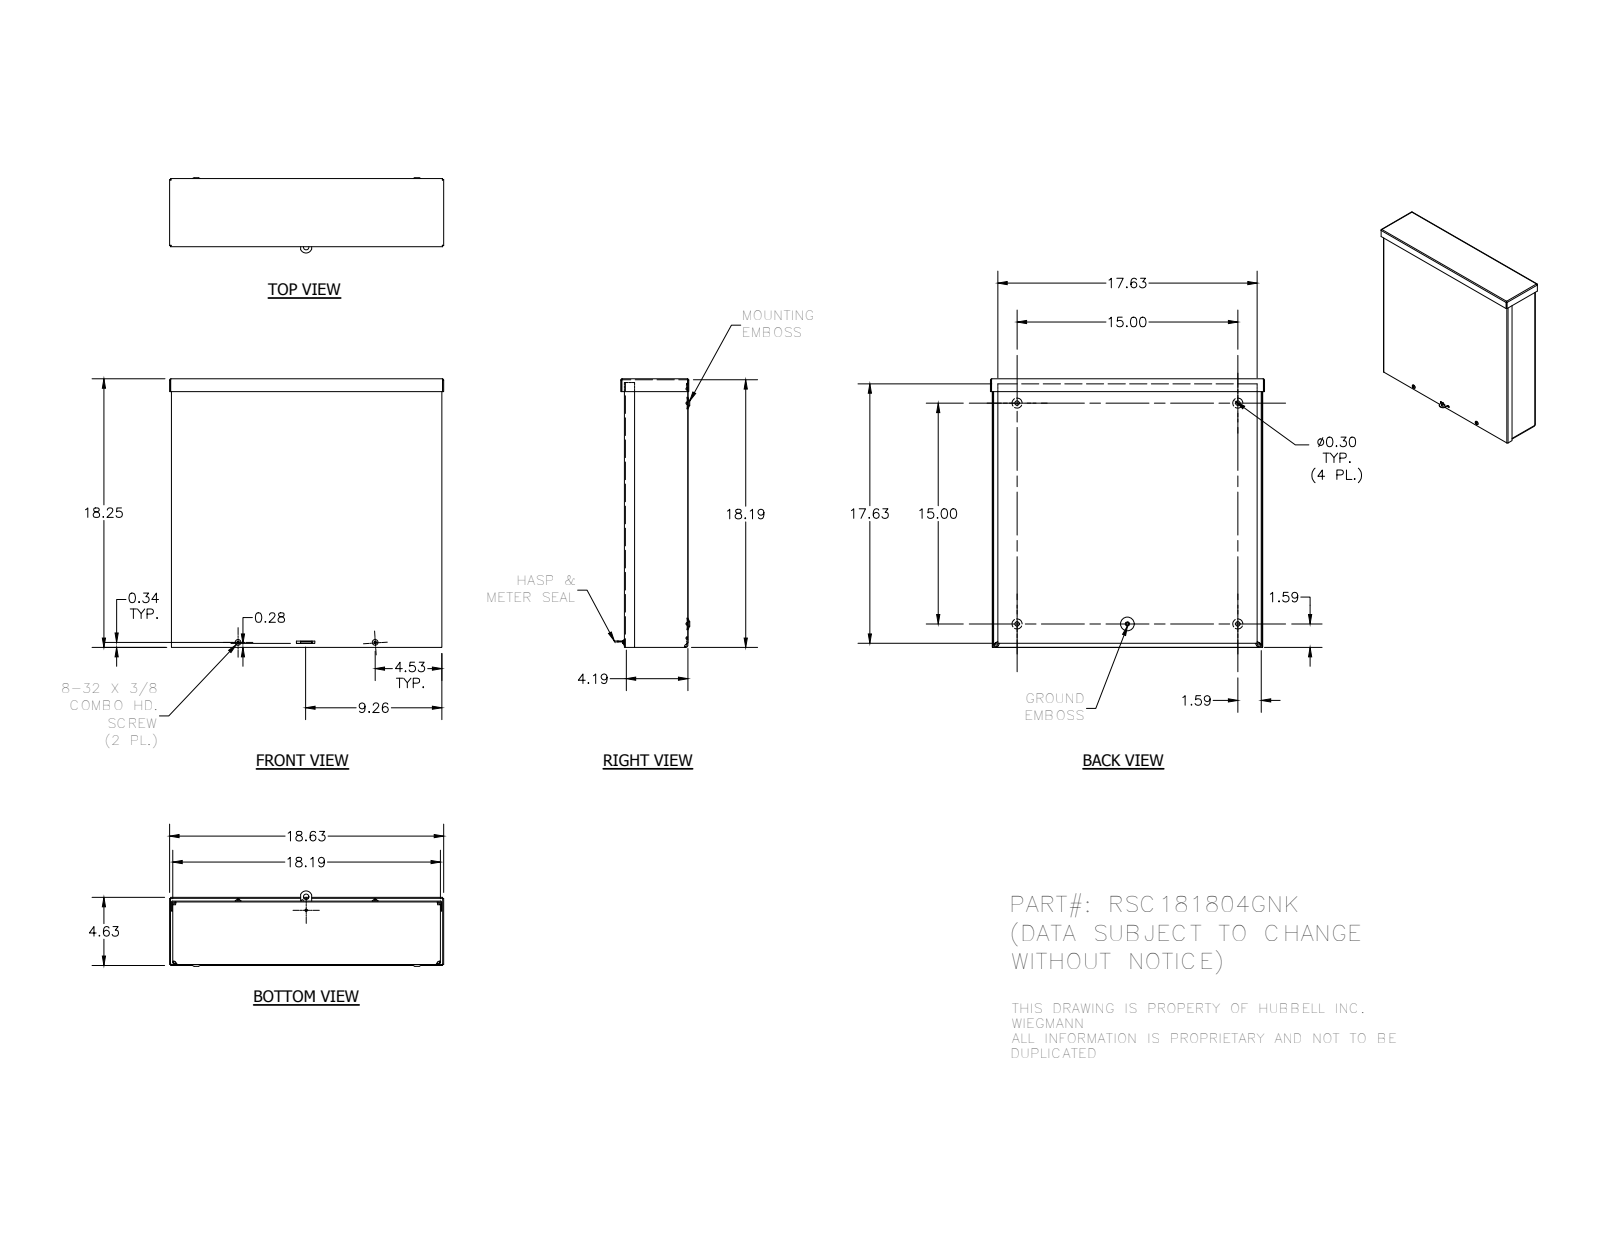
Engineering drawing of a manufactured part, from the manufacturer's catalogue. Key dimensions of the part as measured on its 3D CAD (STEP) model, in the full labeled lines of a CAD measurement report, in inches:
Part name (STEP PRODUCT): RSC181804GNK_WRAP; RSC1818GNK_LID; RSC1804GNK_CAP; 3183 (+3 more)
STEP written by: Autodesk Inventor 2014 (AUTOMOTIVE_DESIGN)
Units: inches
Bodies: 7 solids, 377 faces (163 planar, 78 cylindrical, 136 other)
Overall size (bounding box): 18.625 × 18.25 × 5.125
Volume: 74.02 in³ · Surface area: 2 407 in²
Round holes (diameter × count): ⌀0.3 ×4, ⌀0.313 ×4, ⌀0.125 ×2, ⌀0.148 ×2, ⌀0.156 ×1, ⌀0.165 ×1, ⌀0.375 ×1
Round bosses / shafts (diameter × count): ⌀0.384 ×2, ⌀0.164 ×2, ⌀0.228 ×1
Partial cylindrical surfaces — rounded edges, fillets, slot ends (radius × count): R0.031 ×8, R0.093 ×8, R0.125 ×8, R0.187 ×8, R0.055 ×4, R0.062 ×4, R0.094 ×4, R0.117 ×4
Main face-to-face distances: 0.062, 4.249, 4.187, 0.063, 4.312, 4.25, 18.126, 0.062, 18.188, 0.124
Hole centre spacings: 15, 7.5, 9.313, 16.498, 16.722, 16.77, 17.312, 19.658
